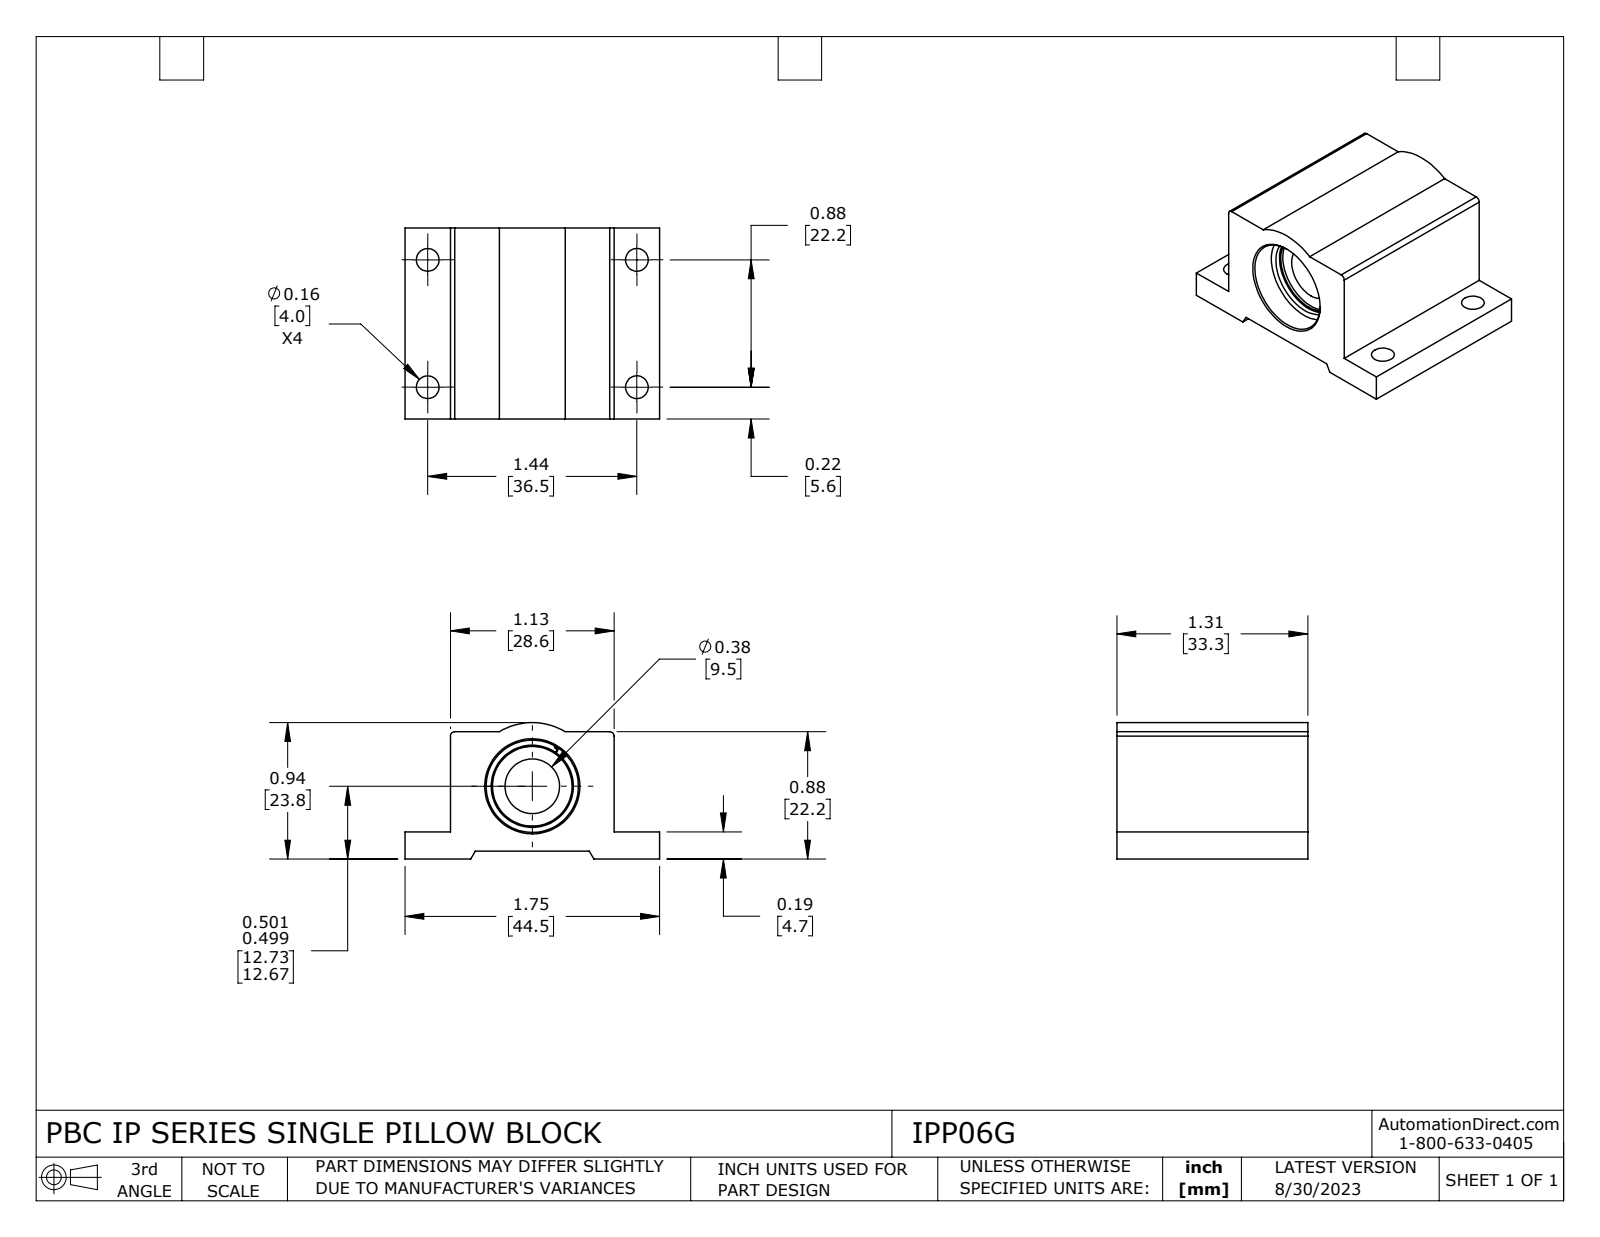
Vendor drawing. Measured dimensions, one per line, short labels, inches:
name: IPP06G
written by: SolidWorks 2021 (CONFIG_CONTROL_DESIGN)
unit: in
bodies: 4 solids, 126 faces (43 planar, 63 cylindrical, 20 other)
size: 1.75 × 1.312 × 0.938
volume: 1.153 in³; area: 15.38 in²
holes: 4× ⌀0.156, 1× ⌀0.375, 1× ⌀0.547, 1× ⌀0.565, 1× ⌀0.634, 1× ⌀0.665
bosses: 1× ⌀0.675, 1× ⌀0.625, 1× ⌀0.588
rounds: 4× R0.009, 2× R0.004, 2× R0.014, 2× R0.03, 1× R0.438
face distances: 0.055, 1.125, 0.875, 0.82, 0.187, 0.132, 0.688, 1.313, 0.313, 1.438
hole spacings: 0.875, 1.438, 1.683
